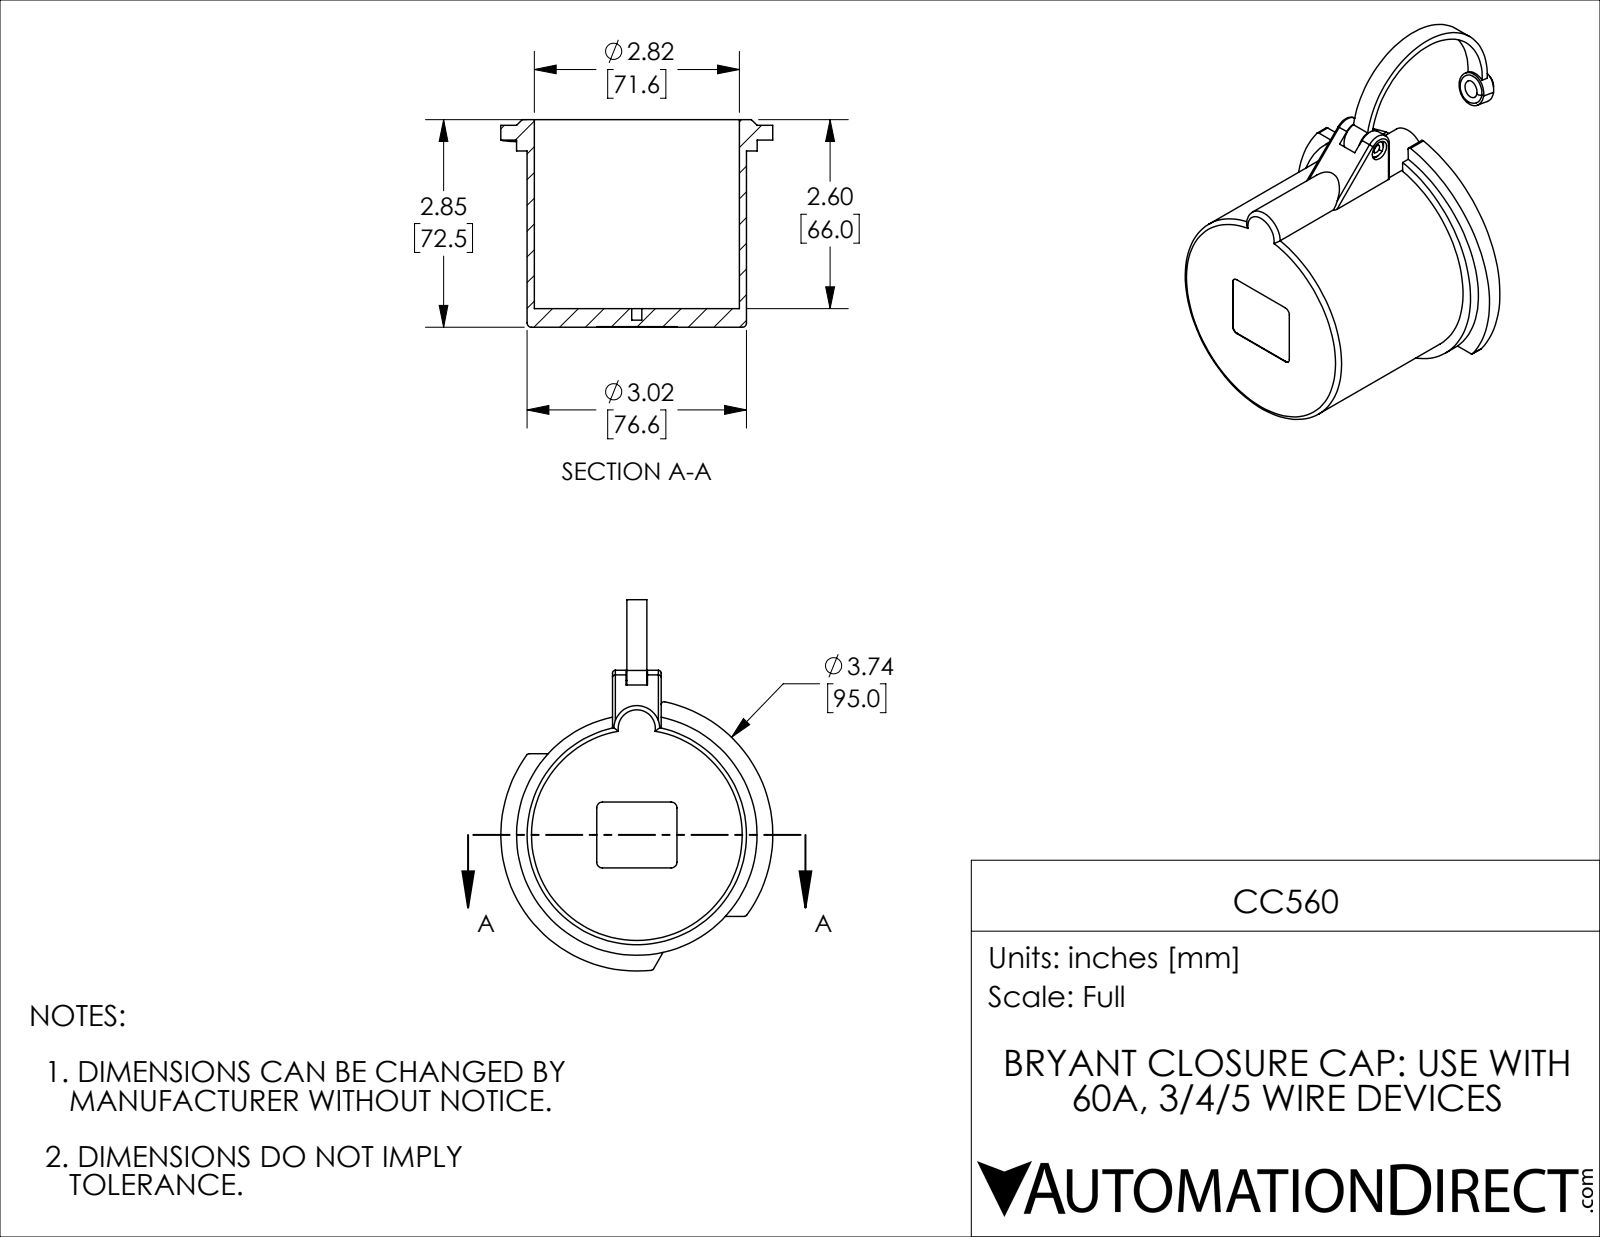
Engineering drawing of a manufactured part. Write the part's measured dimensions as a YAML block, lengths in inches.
part_name: "CC560"
step_written_by: "SolidWorks 2021 (CONFIG_CONTROL_DESIGN)"
units: inches
bodies: {solids: 1, faces: 126, planar: 39, cylindrical: 69, other: 18}
overall_size: [5.104, 4.406, 3.74]
volume: 5.546
surface_area: 79.18
round_holes:
  - {diameter: 0.118, count: 1}
  - {diameter: 0.138, count: 1}
  - {diameter: 0.169, count: 1}
  - {diameter: 0.197, count: 1}
  - {diameter: 0.244, count: 1}
  - {diameter: 0.276, count: 1}
  - {diameter: 2.819, count: 1}
round_bosses_or_shafts:
  - {diameter: 3.307, count: 1}
  - {diameter: 3.016, count: 1}
  - {diameter: 0.472, count: 1}
  - {diameter: 0.433, count: 1}
  - {diameter: 0.276, count: 1}
  - {diameter: 0.236, count: 1}
  - {diameter: 0.157, count: 1}
partial_cylinders:
  - {radius: 0.039, count: 8}
  - {radius: 0.079, count: 4}
  - {radius: 0.197, count: 1}
  - {radius: 0.315, count: 1}
  - {radius: 1.074, count: 1}
  - {radius: 1.173, count: 1}
  - {radius: 1.87, count: 1}
face_to_face_distances: [0.256, 2.776, 2.52, 0.079, 2.854, 2.598, 0.354, 2.421, 2.165, 0.433]
